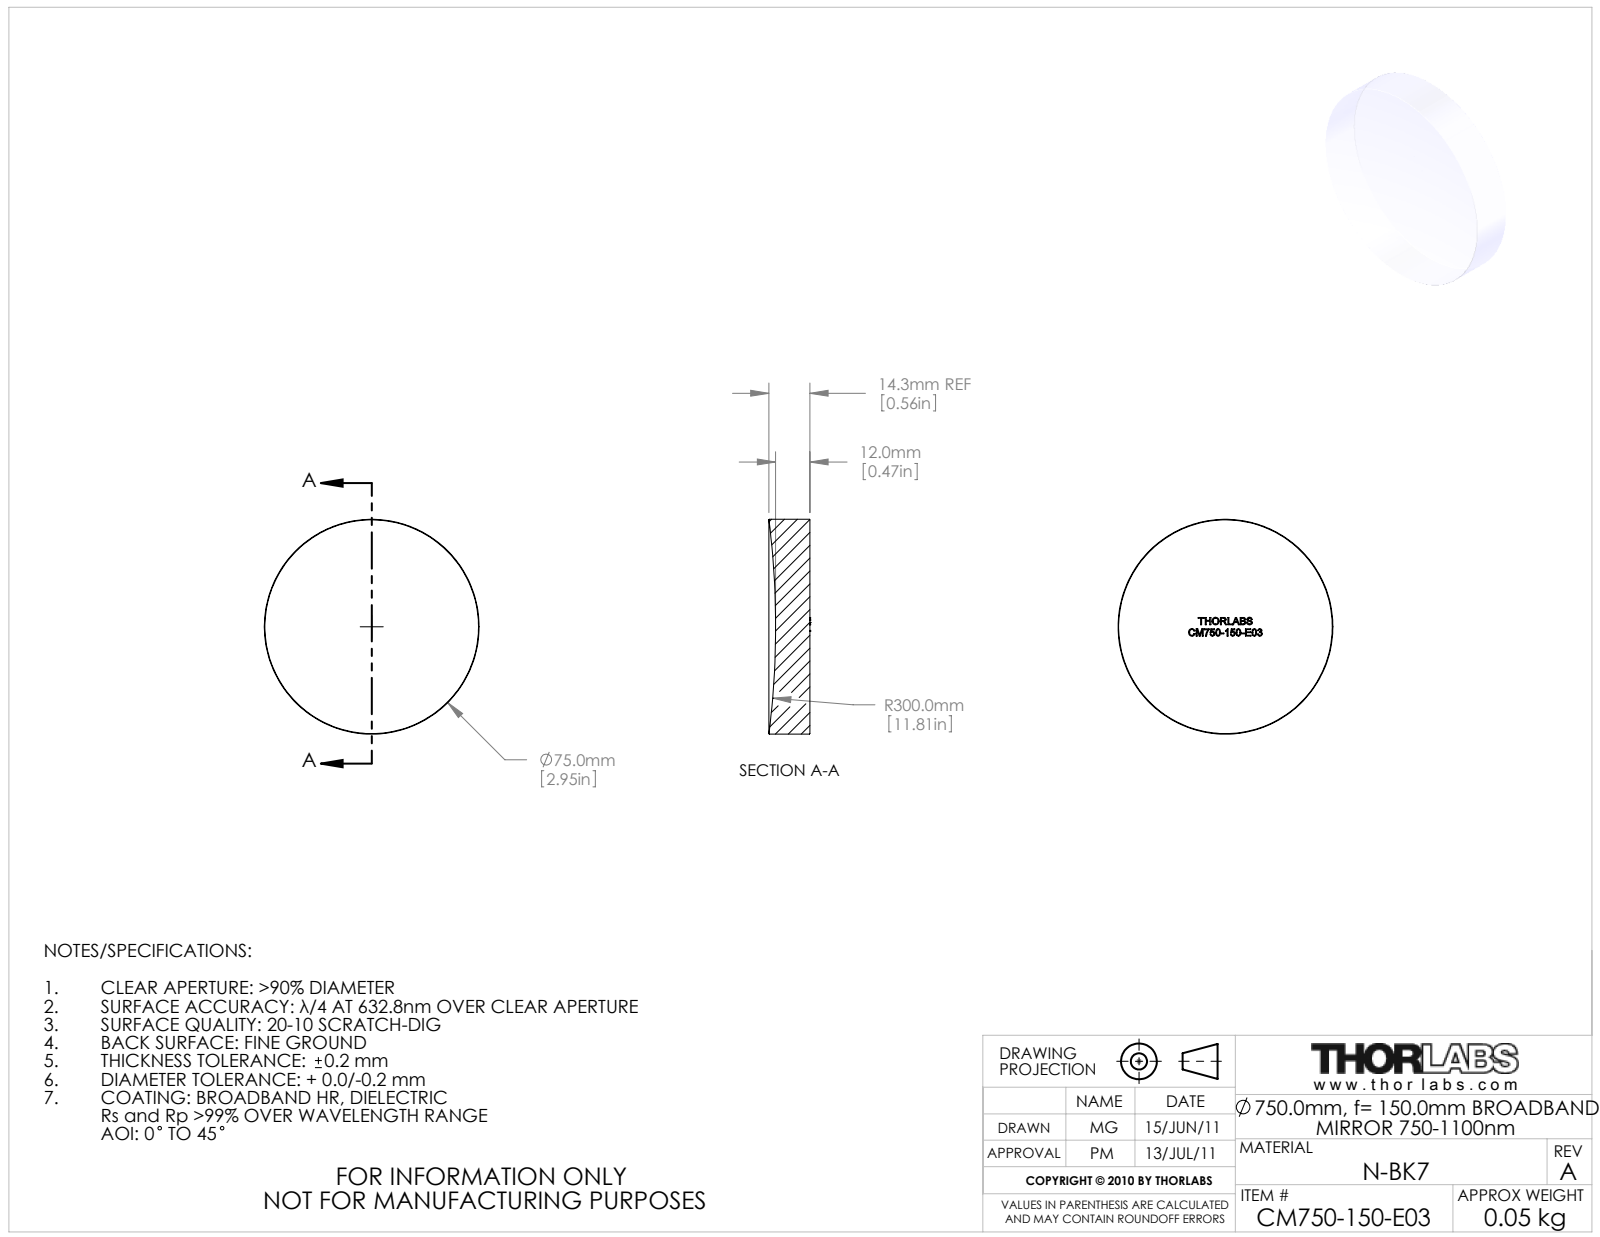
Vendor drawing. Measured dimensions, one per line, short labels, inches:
name: 22650-E0W
written by: SolidWorks 2011 (AUTOMOTIVE_DESIGN)
unit: in
bodies: 0 solids, 40 faces (31 planar, 2 cylindrical, 7 other)
size: 2.953 × 2.953 × 0.564
bosses: 1× ⌀2.953
